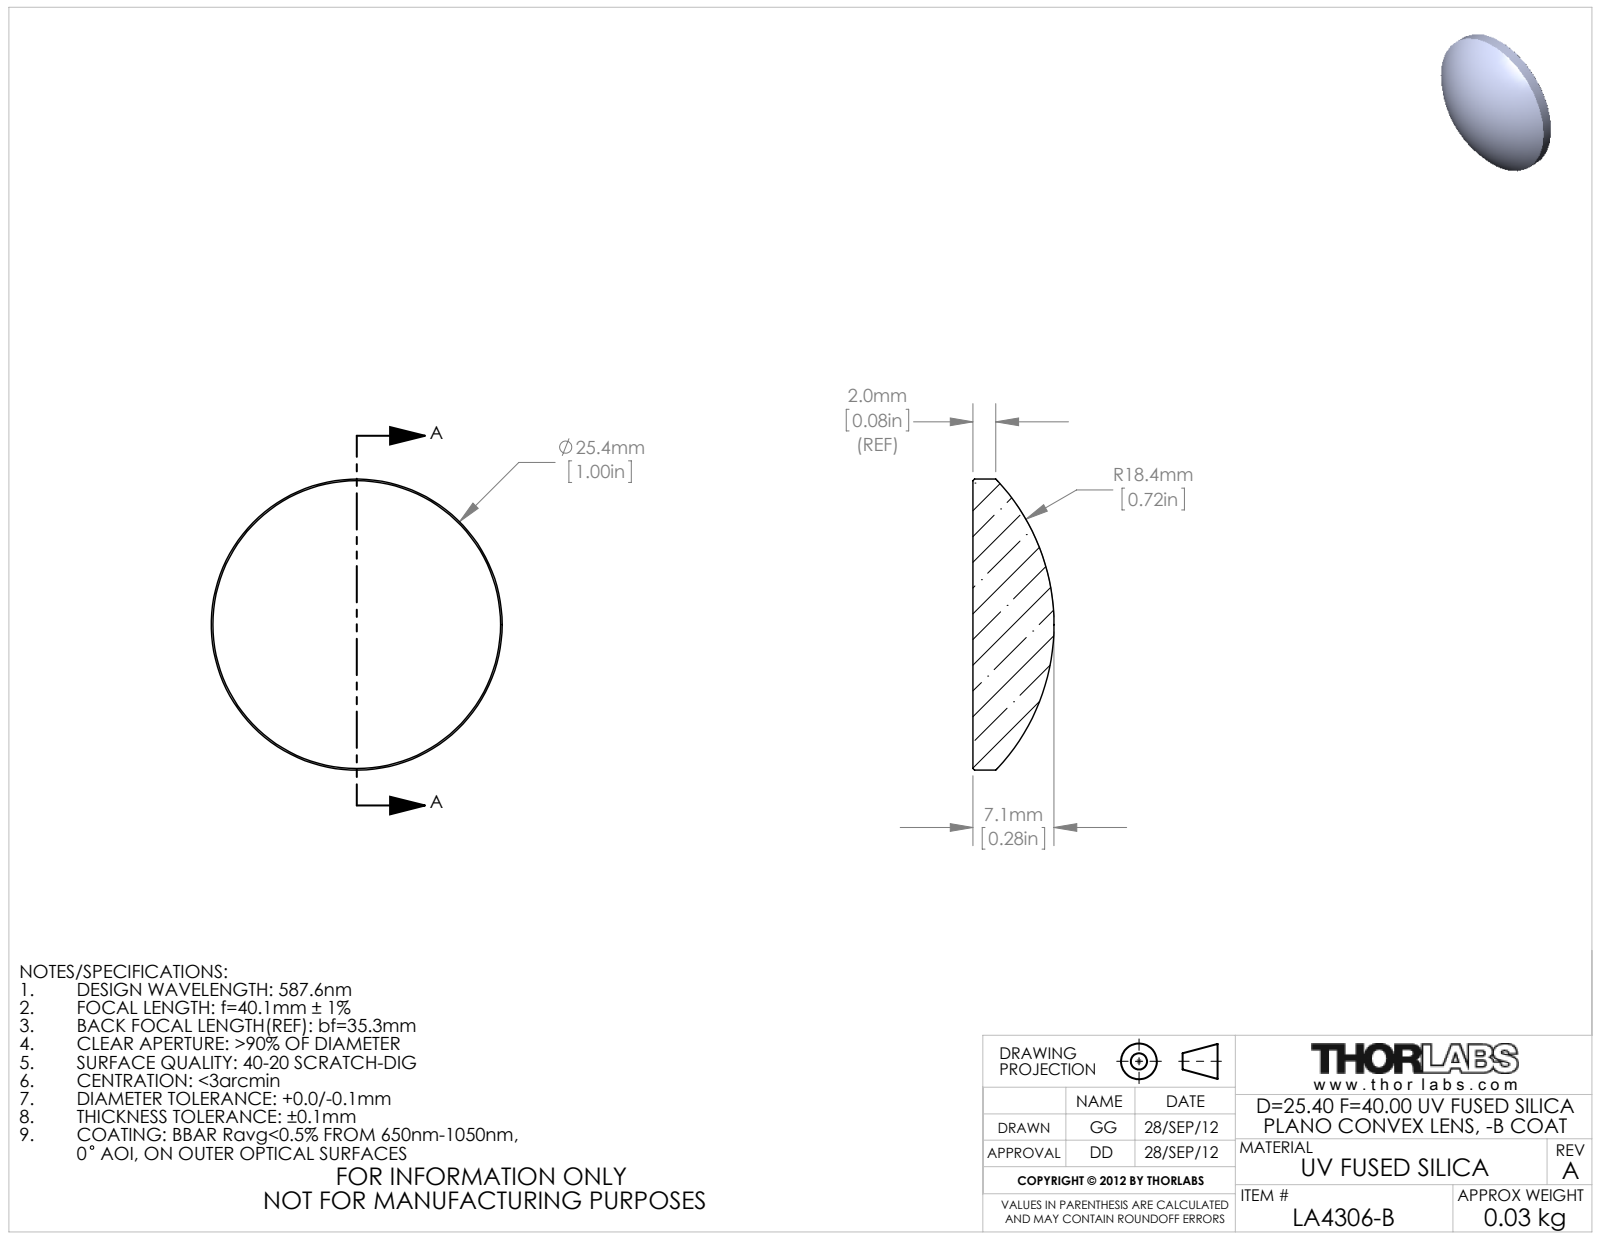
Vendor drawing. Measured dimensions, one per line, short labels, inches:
name: 24997-E0W
written by: SolidWorks 2011 (CONFIG_CONTROL_DESIGN)
unit: in
bodies: 1 solid, 9 faces (1 planar, 2 cylindrical, 6 other)
size: 1 × 1 × 0.279
volume: 0.145 in³; area: 1.933 in²
bosses: 1× ⌀1
